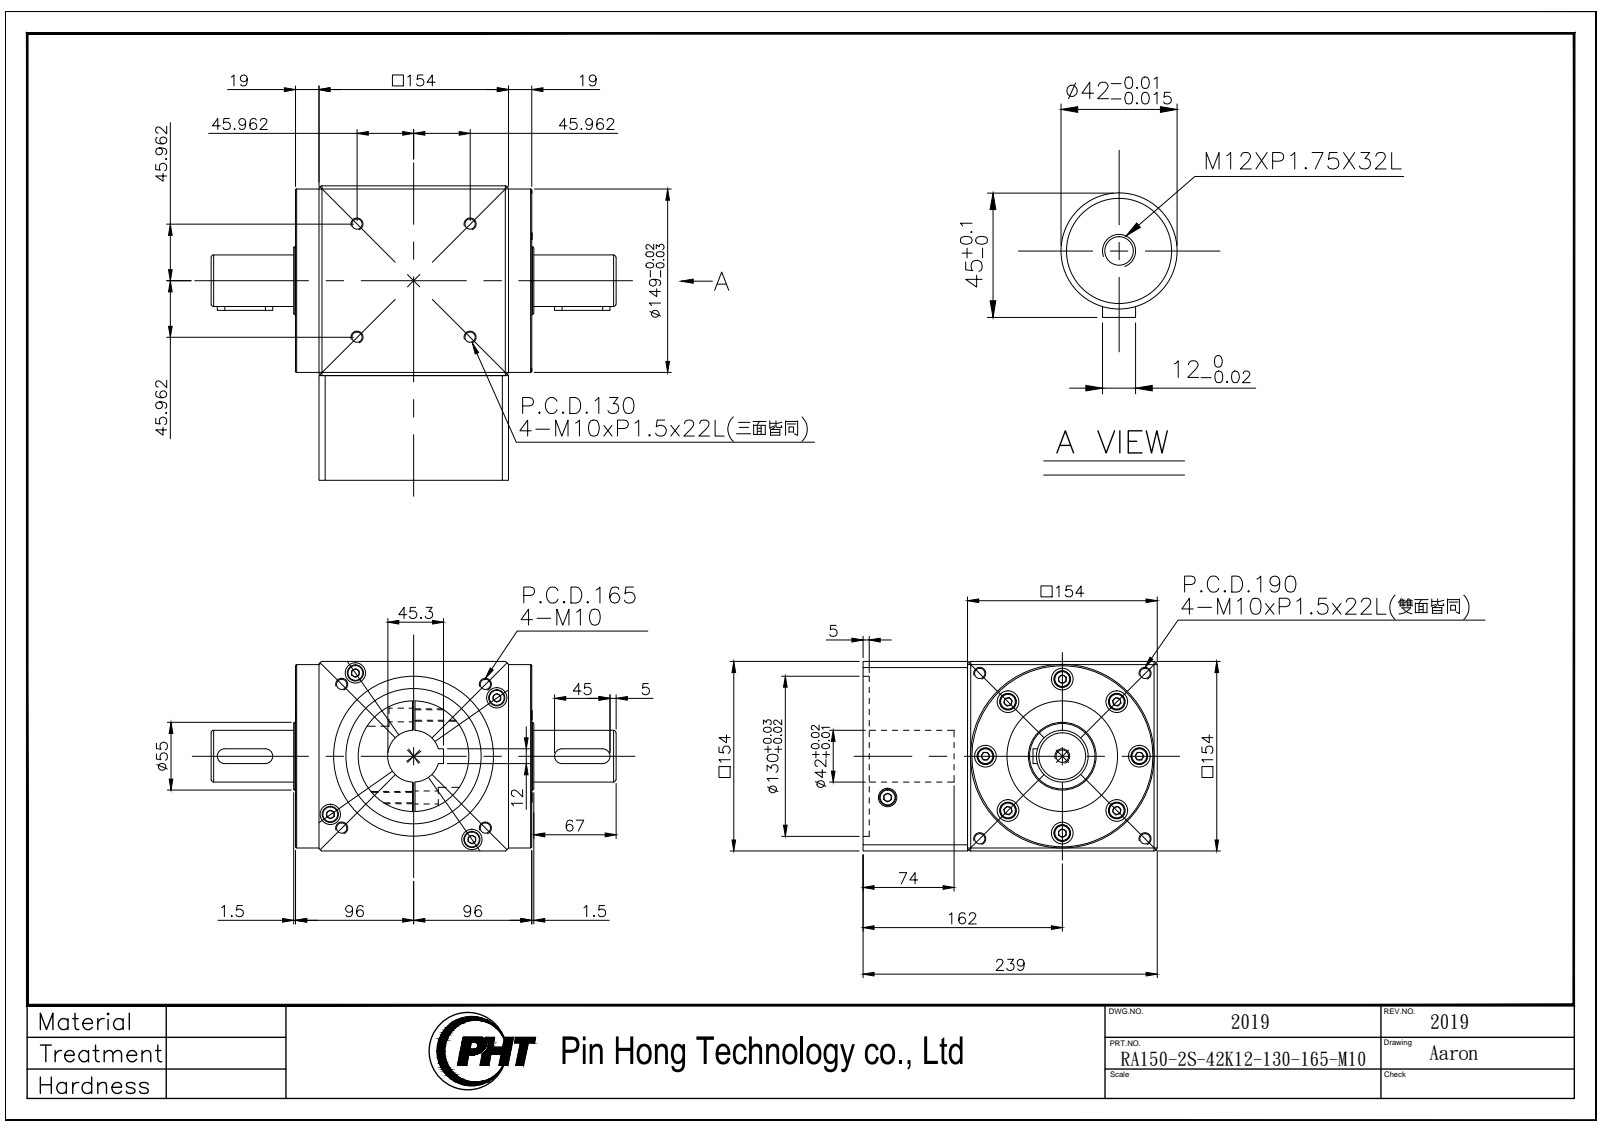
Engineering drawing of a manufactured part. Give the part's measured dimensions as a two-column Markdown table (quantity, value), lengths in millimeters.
| quantity | value |
| --- | --- |
| part name | RA150-2S-42K12-130-165-M10_2019 |
| STEP written by | SolidWorks 2016 (AUTOMOTIVE_DESIGN) |
| units | millimeters |
| bodies | 3 solids, 712 faces (348 planar, 220 cylindrical, 144 other) |
| overall size | 329 × 239 × 154 |
| volume | 5 990 000 mm³ |
| surface area | 358 171 mm² |
| round holes (diameter × count) | 8.5 × 16, 11 × 12, 17.5 × 8, 16.5 × 4, 15 × 2, 4.08 × 1, 10.2 × 1, 42 × 1, 110 × 1, 130 × 1 |
| round bosses / shafts (diameter × count) | 16 × 12, 90 × 2, 149 × 1, 55 × 1, 42 × 1 |
| partial cylindrical surfaces (radius × count) | 6 × 4, 107.4 × 1 |
| main face-to-face distances | 154, 19, 173, 239, 192, 95, 19.1, 173.1, 192.1, 76 |
| hole center spacings | 47.83, 67.34, 91.92, 105.03, 113.72, 115.48, 146.05, 14.38 |
